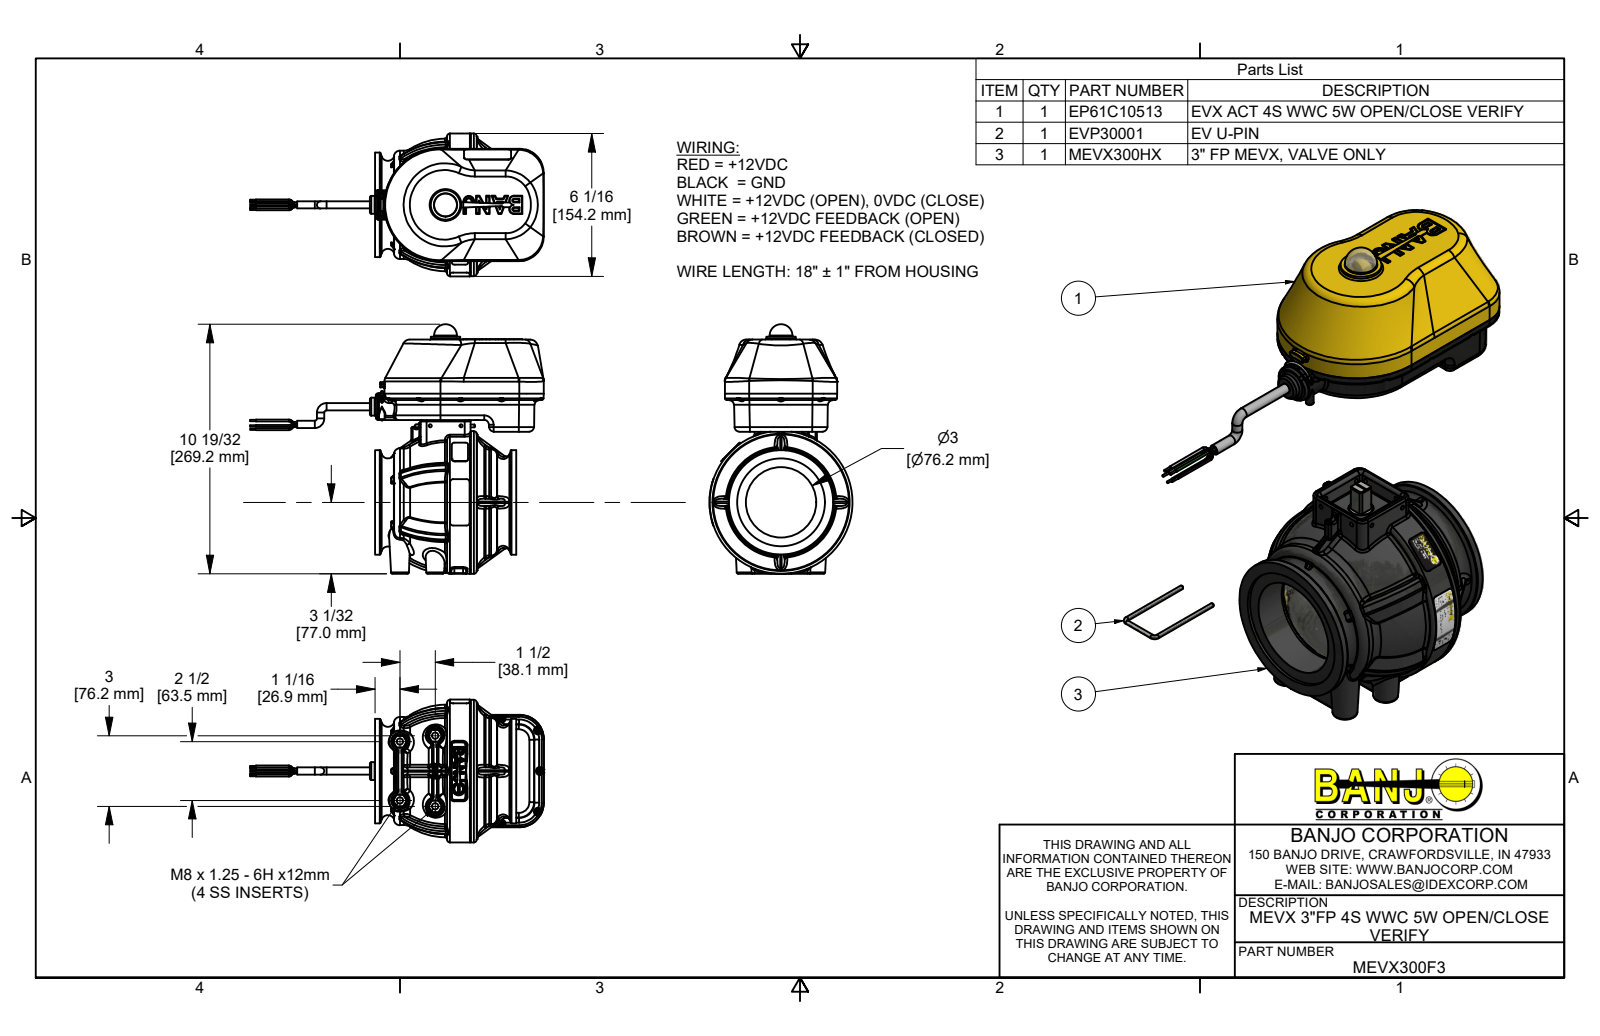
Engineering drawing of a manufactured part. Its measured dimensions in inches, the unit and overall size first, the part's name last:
Units: inches
Overall size (bounding box): 12.476 × 10.6 × 6.072
Round holes (diameter × count): ⌀0.15 ×15, ⌀0.095 ×11, ⌀0.34 ×11, ⌀0.08 ×7, ⌀0.135 ×6, ⌀0.104 ×4, ⌀0.136 ×4, ⌀0.176 ×4, ⌀0.262 ×4, ⌀0.266 ×4, ⌀0.433 ×4, ⌀0.148 ×3
Round bosses / shafts (diameter × count): ⌀0.08 ×25, ⌀0.25 ×19, ⌀0.14 ×11, ⌀0.108 ×11, ⌀0.085 ×11, ⌀0.058 ×10, ⌀0.437 ×4, ⌀0.375 ×4
Partial cylindrical surfaces — rounded edges, fillets, slot ends (radius × count): R0.013 ×204, R0.405 ×138, R0.387 ×114, R0.309 ×112, R0.253 ×108, R0.01 ×106, R0.609 ×106, R0.04 ×46
Main face-to-face distances: 0.083, 0.5, 0.085, 0.181, 0.096, 2.175, 2.356, 2.271, 0.125, 0.1
Hole centre spacings: 3.316, 2.272, 1.313, 1.465, 1.624, 1.69, 2.315, 4.245
Volume: 89.68 in³ · Surface area: 902.1 in²
Bodies: 81 solids, 8396 faces (2916 planar, 3198 cylindrical, 2282 other)
Part name (STEP PRODUCT): MEVX300F3; EP61C10513; B61905PPHS; B632038PM (+8 more)
STEP written by: Autodesk Inventor 2021 (AUTOMOTIVE_DESIGN)
